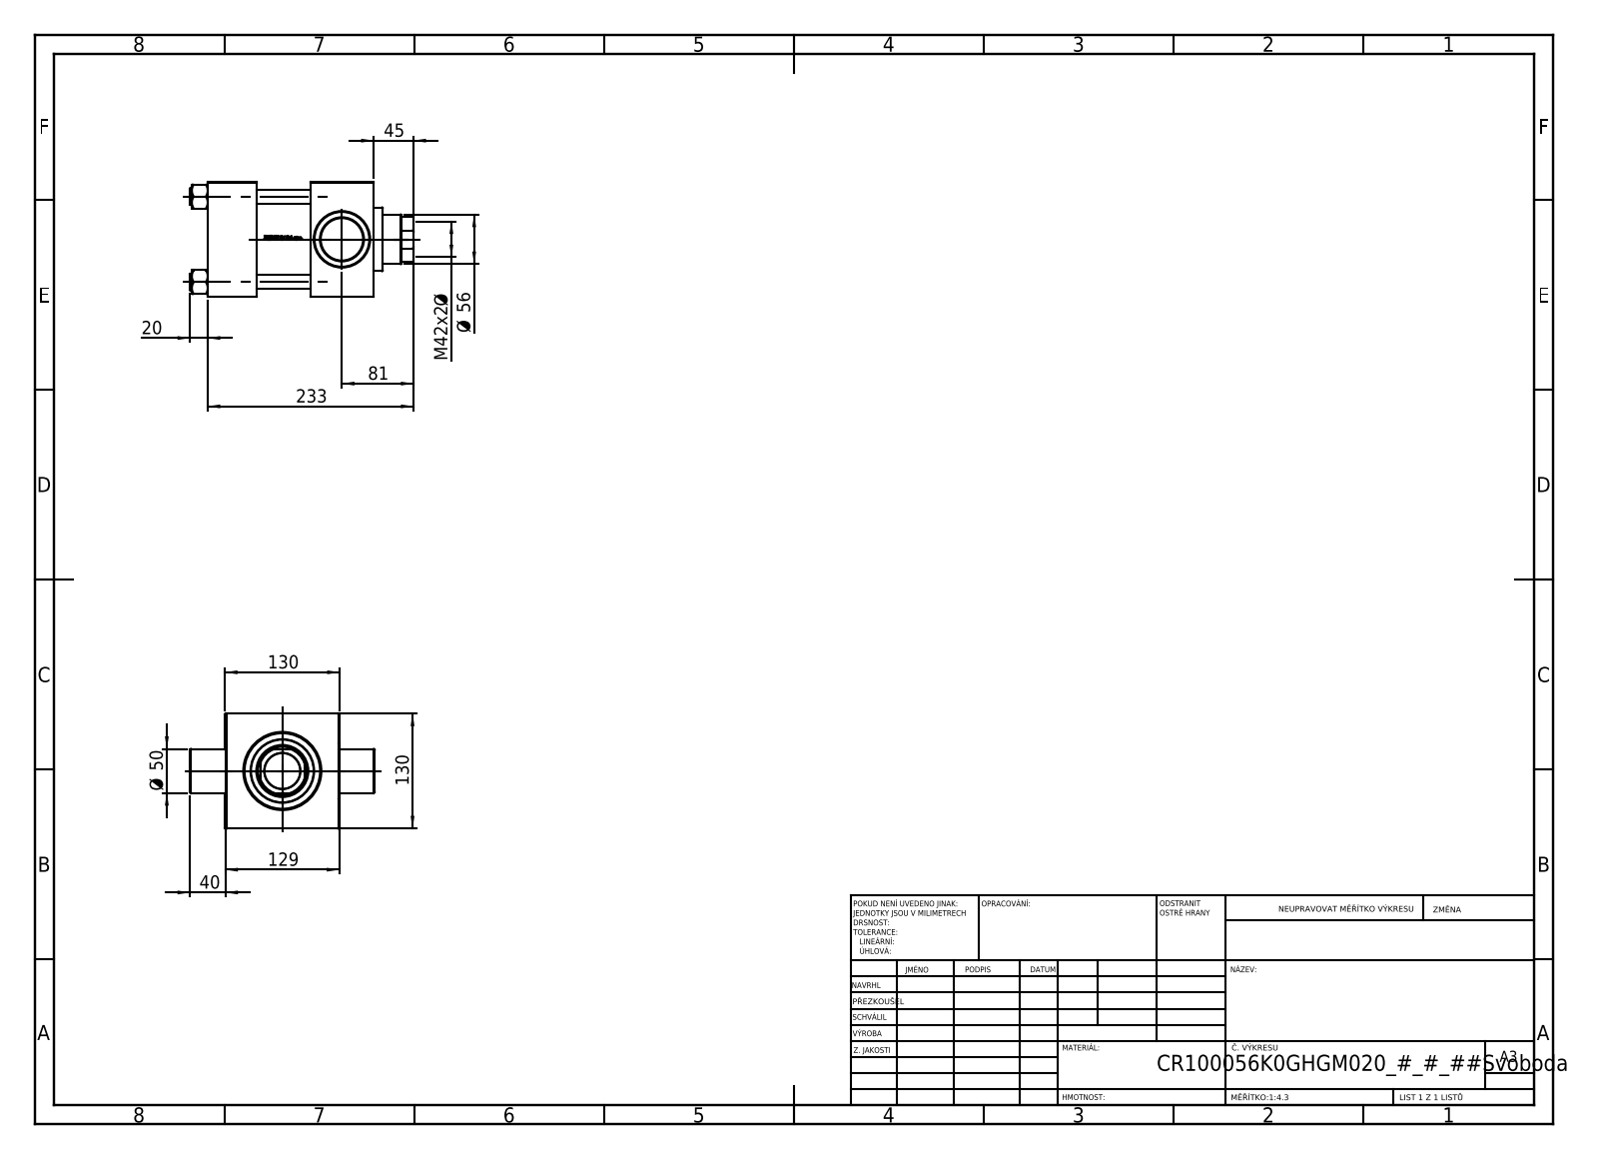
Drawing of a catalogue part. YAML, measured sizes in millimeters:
part_name: "V215_VC_A; NUT_M5_K; V215CR_K_Body; V215CR_K_TYCINKA (+1 more)"
step_written_by: "SolidWorks 2019 (CONFIG_CONTROL_DESIGN)"
units: millimeters
bodies: {solids: 11, faces: 1107, planar: 475, cylindrical: 110, other: 522}
overall_size: [253, 209, 130]
volume: 2802000
surface_area: 334803
round_holes:
  - {diameter: 16, count: 4}
  - {diameter: 7, count: 1}
  - {diameter: 40.5, count: 1}
  - {diameter: 56, count: 1}
  - {diameter: 59, count: 1}
  - {diameter: 76, count: 1}
  - {diameter: 85.5, count: 1}
  - {diameter: 100, count: 1}
round_bosses_or_shafts:
  - {diameter: 19, count: 4}
  - {diameter: 106, count: 1}
  - {diameter: 72, count: 1}
  - {diameter: 50, count: 1}
partial_cylinders:
  - {radius: 27, count: 1}
face_to_face_distances: [130, 55, 128.5, 1.5, 188, 133, 61, 116, 72, 127]
hole_center_spacings: [68.52, 96.9, 137.04]
